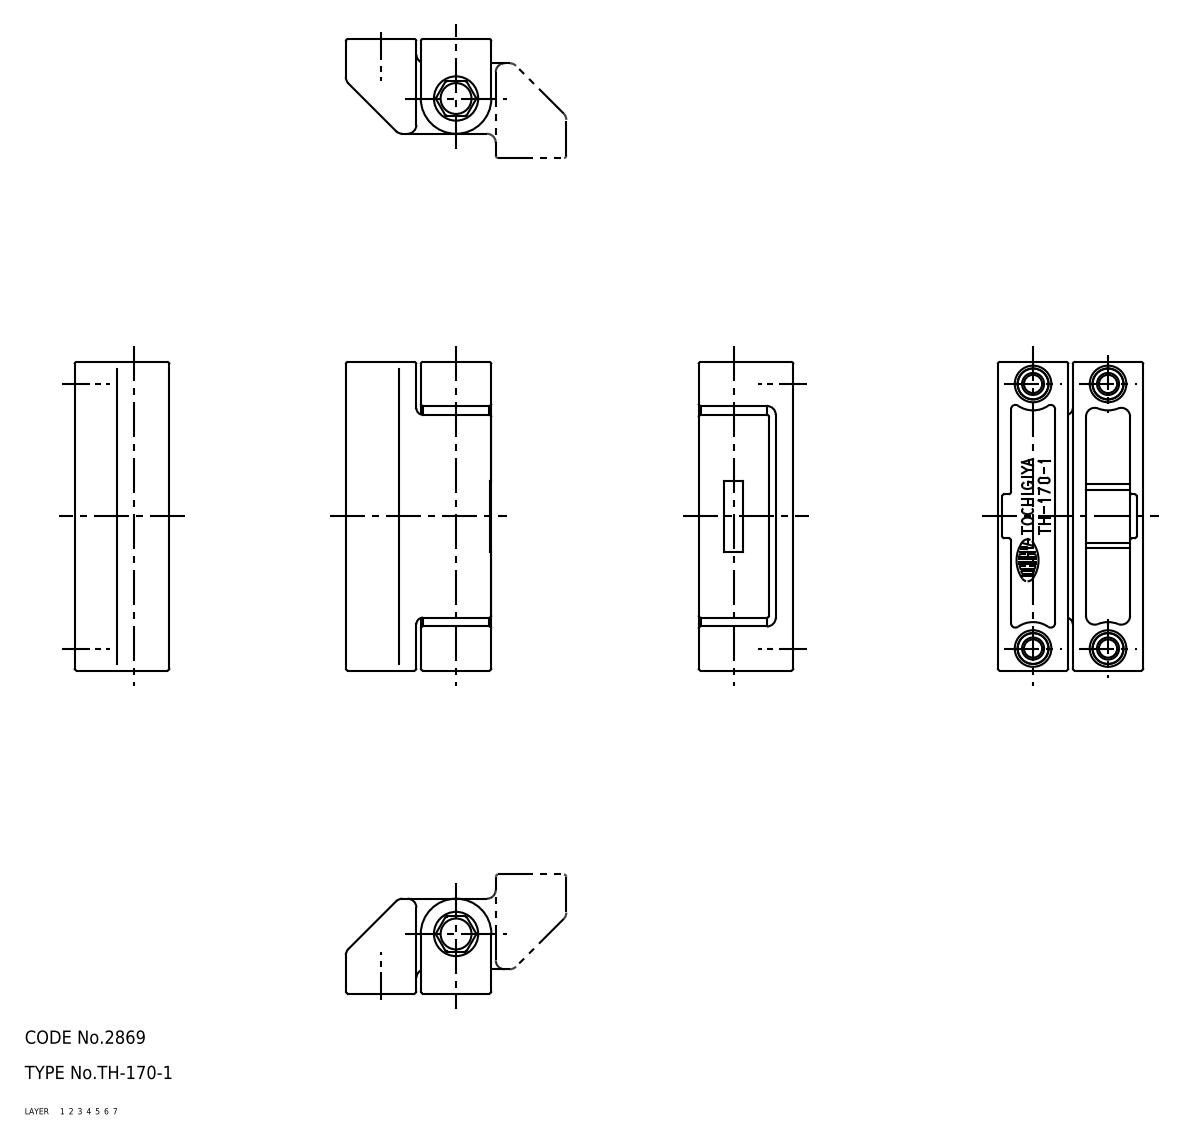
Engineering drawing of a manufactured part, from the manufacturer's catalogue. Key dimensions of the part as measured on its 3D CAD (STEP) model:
Part name (STEP PRODUCT): 67121856; 67121869; 67121882; 67121895
STEP written by: CADfix (AUTOMOTIVE_DESIGN)
Units: millimetres
Bodies: 4 solids, 255 faces (0 planar, 0 cylindrical, 255 other)
Overall size (bounding box): 70 × 33 × 21.5
Volume: 32 687 mm³ · Surface area: 16 995 mm²
